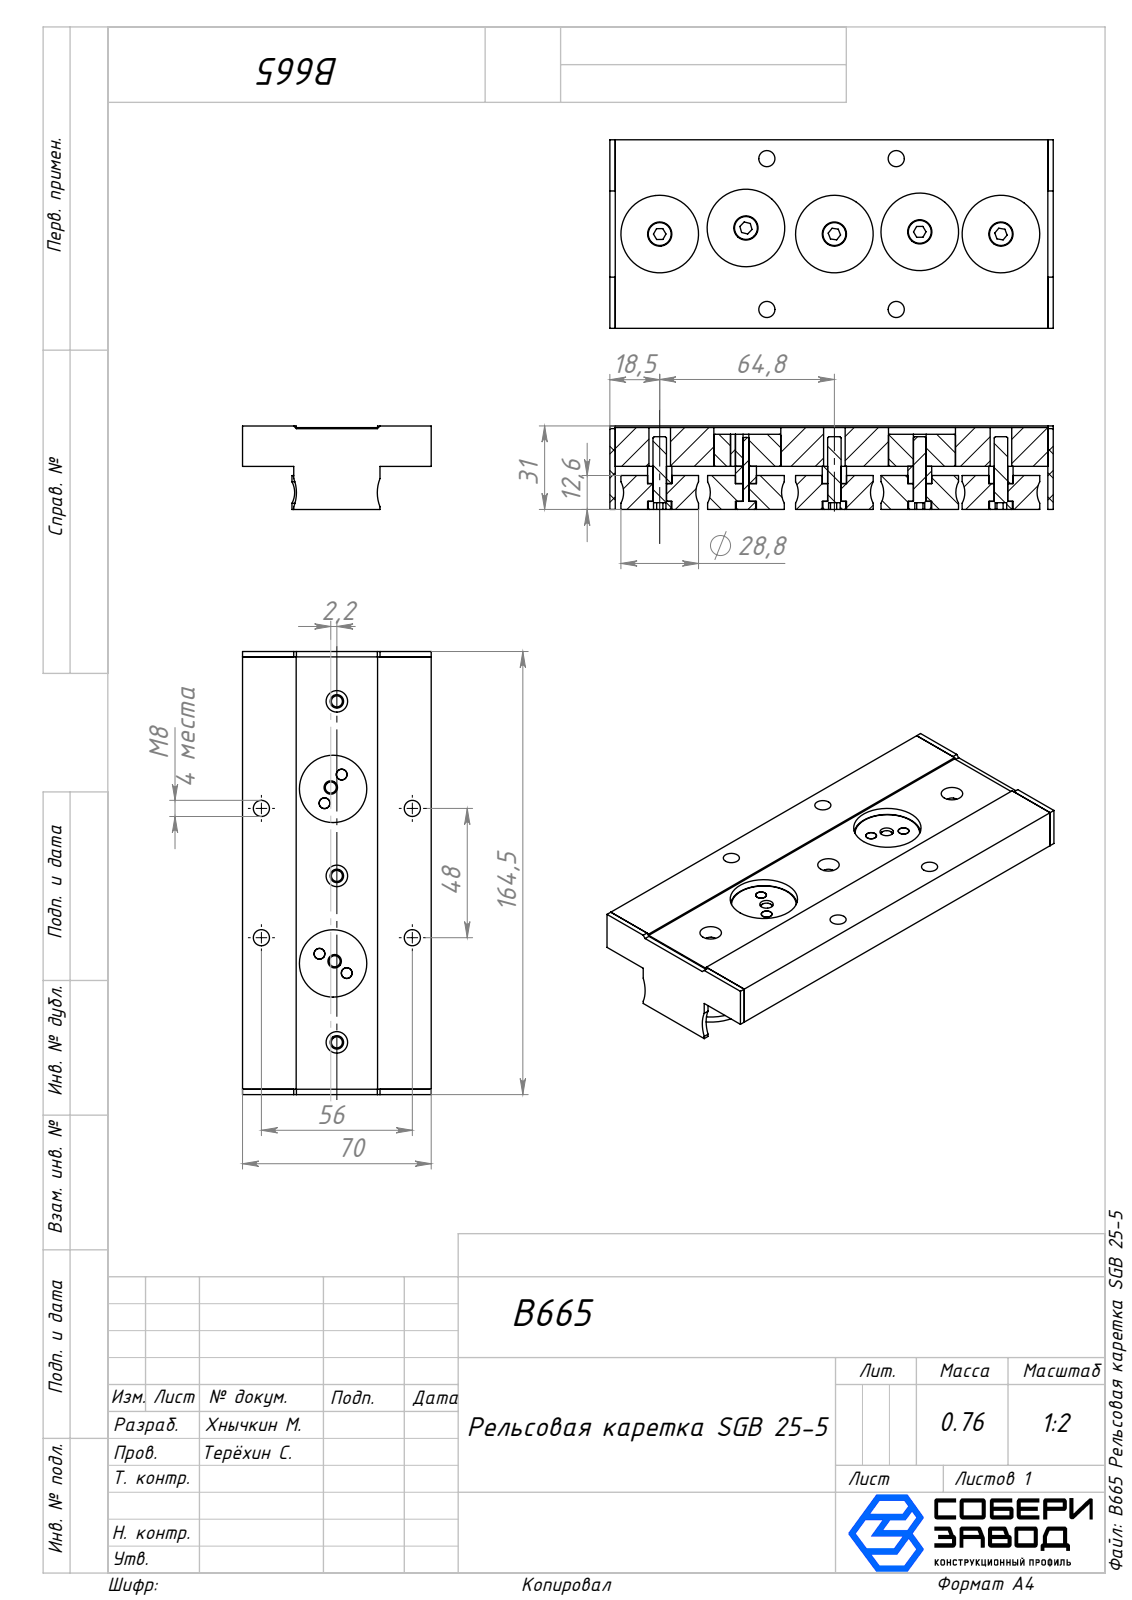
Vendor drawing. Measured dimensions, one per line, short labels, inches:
name: B665 Заслонка_00; B665 Деталь для настройки смещения оси_00; B665 Винт_00; B665 Дистанционная втулка_00 (+3 more)
written by: SolidWorks 2025 (AUTOMOTIVE_DESIGN)
unit: in
bodies: 24 solids, 330 faces (134 planar, 138 cylindrical, 58 other)
size: 6.476 × 2.756 × 1.22
volume: 12.54 in³; area: 95.86 in²
holes: 5× ⌀0.197, 5× ⌀0.354, 4× ⌀0.157, 4× ⌀0.236, 3× ⌀0.315, 2× ⌀0.984
bosses: 5× ⌀1.134, 5× ⌀0.335
rounds: 2× R0.562
face distances: 0.591, 0.567, 0.024, 1.22, 1.197, 0.63, 0.079, 6.398, 0.134, 0.724
hole spacings: 0.244, 0.039, 0.247, 1.281, 1.425, 1.479, 1.885, 1.89
